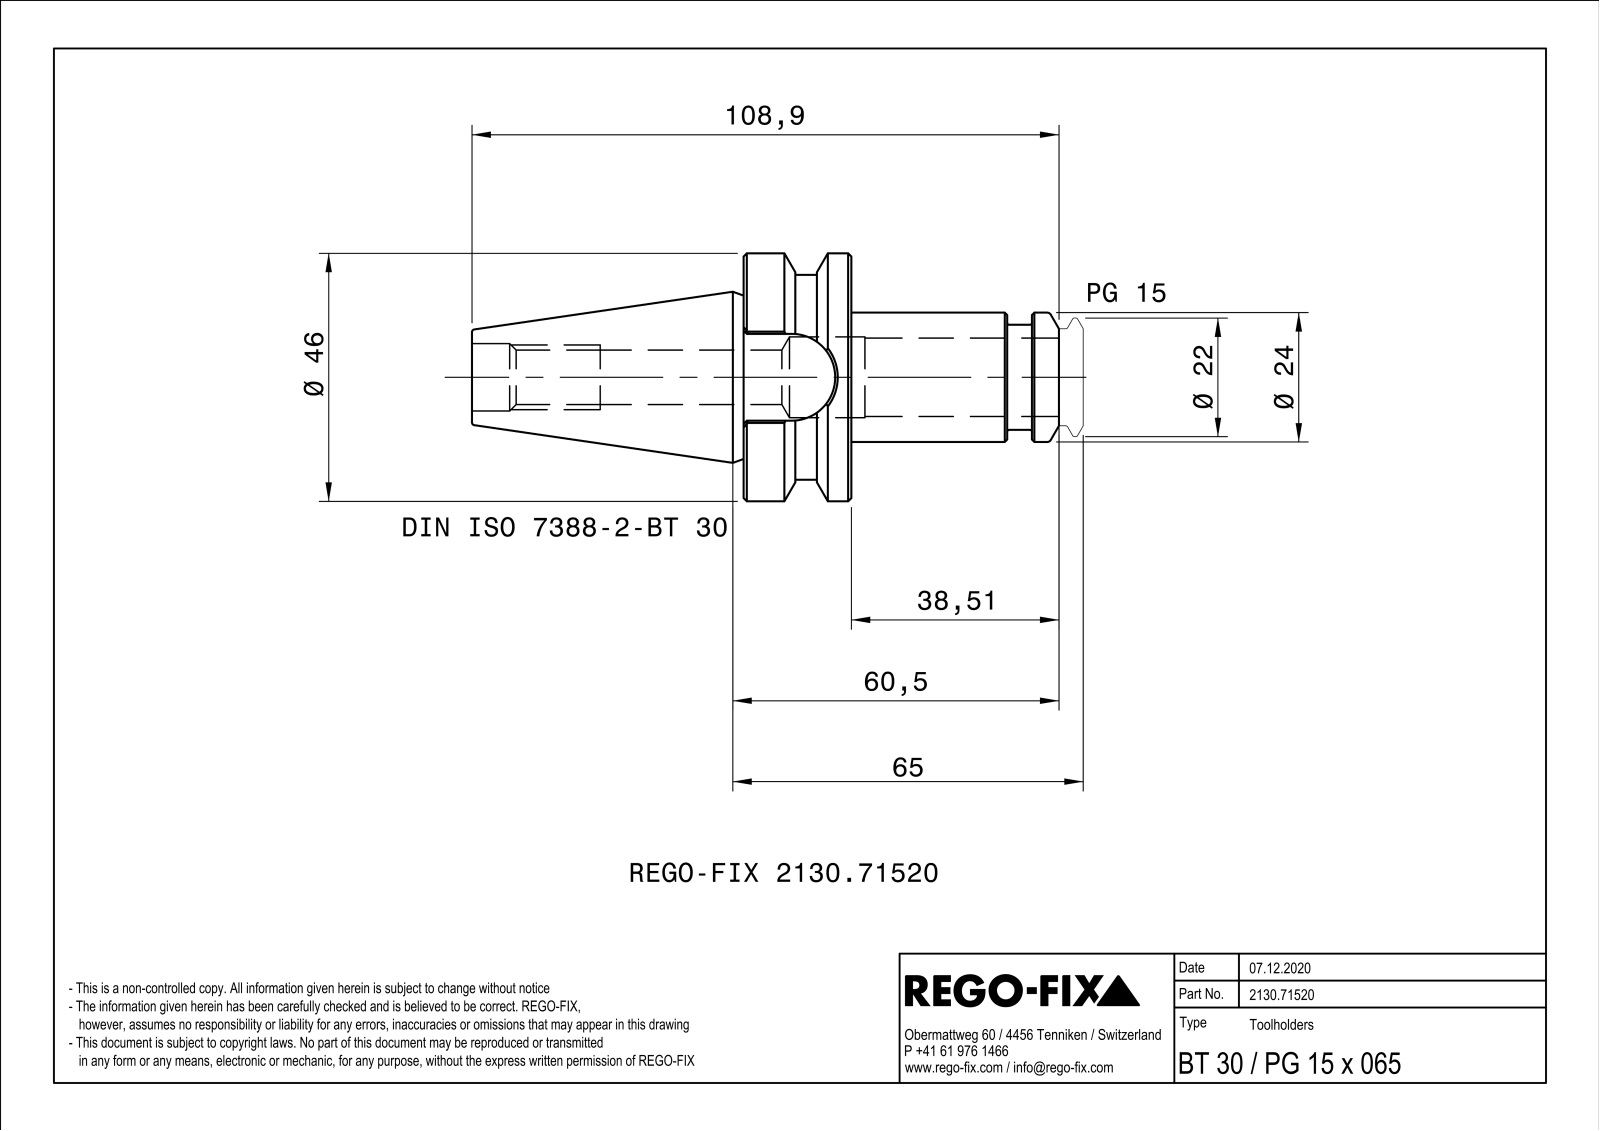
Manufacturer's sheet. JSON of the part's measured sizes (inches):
{"part_name": "NOCUT", "step_written_by": "SIEMENS PLM Software Solid Edge ST10 (AUTOMOTIVE_DESIGN)", "units": "inches", "bodies": {"solids": 1, "faces": 91, "planar": 34, "cylindrical": 22, "other": 35}, "overall_size": [4.287, 1.811, 1.811], "volume_in3": 3.411, "surface_area_in2": 26.31, "round_holes": [[0.398, 1], [0.492, 1], [0.591, 1]], "round_bosses_or_shafts": [[1.811, 1], [0.945, 1], [0.768, 1]], "partial_cylinders_radius": [[0.02, 8], [0.317, 1], [0.748, 1]], "face_to_face_distances": [0.787, 1.28, 1.925, 1.138, 0.181, 1.319, 2.106, 0.634, 4.091, 3.909]}
